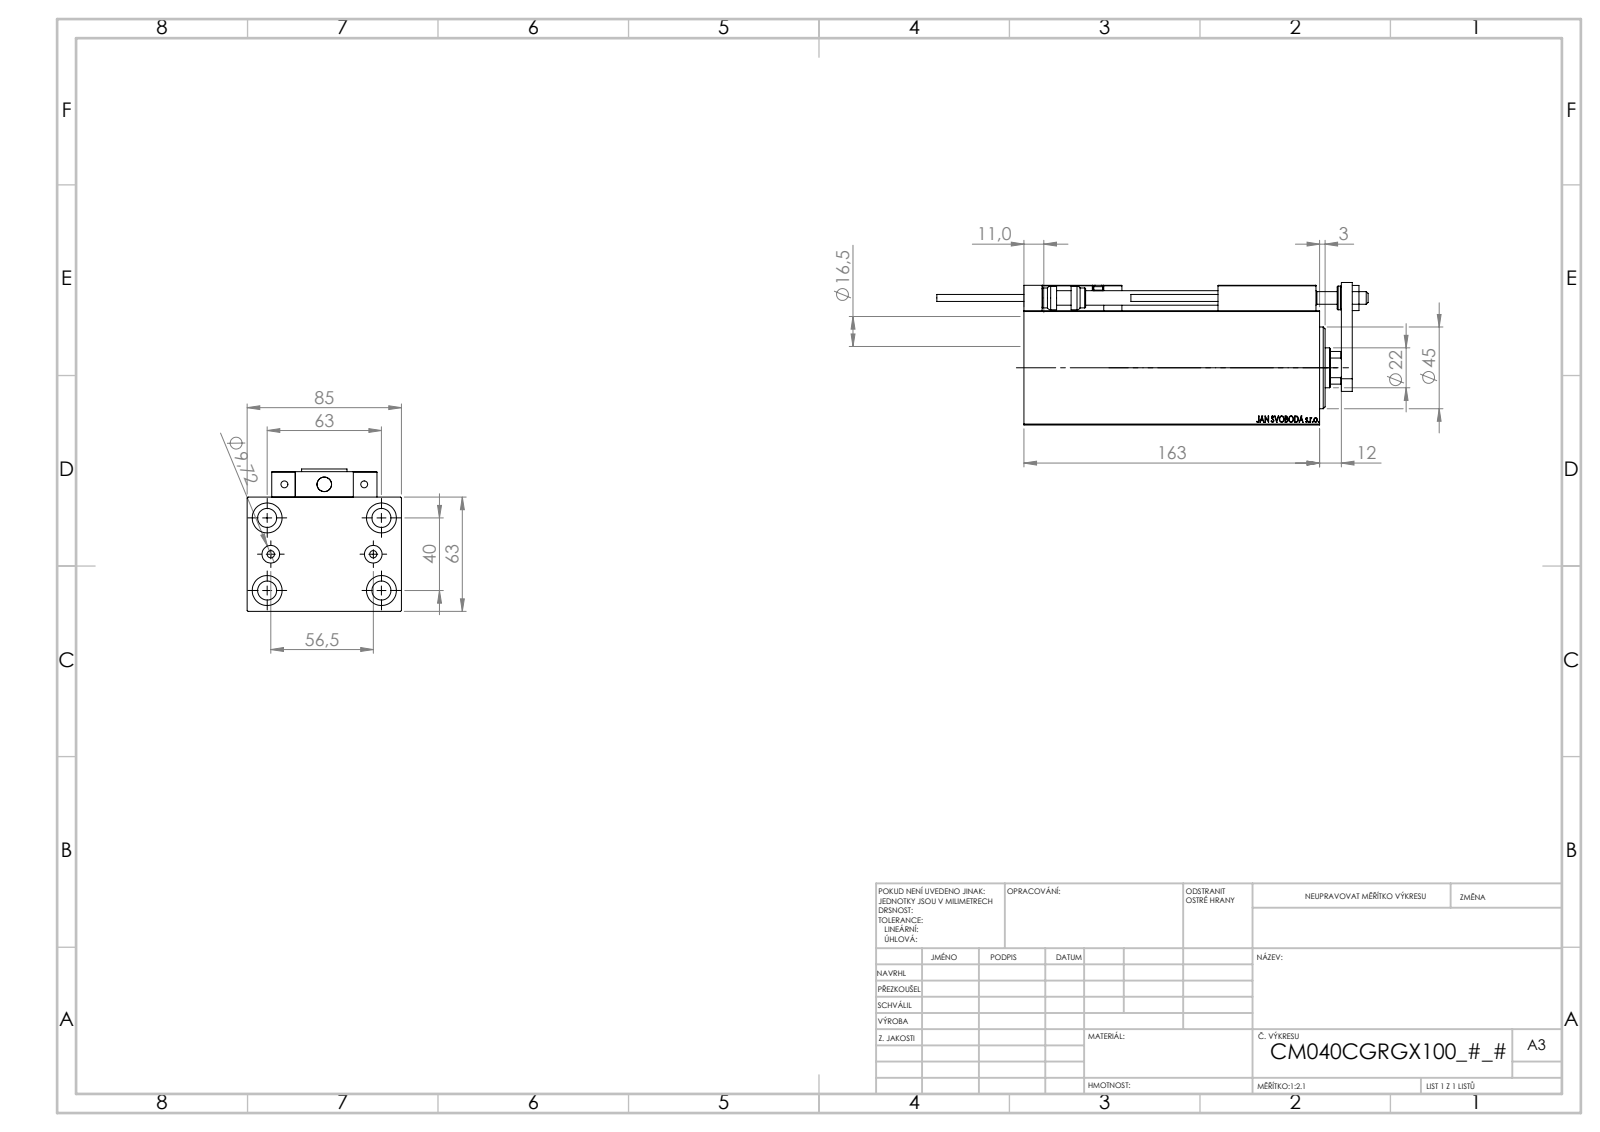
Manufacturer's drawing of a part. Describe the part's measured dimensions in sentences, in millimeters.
The part is named "ZARAZKA; Block; KONCOVKA; SWITCH X (+7 more)". Its 3-D file was written by "SolidWorks 2019 (CONFIG_CONTROL_DESIGN)". It is 23 solids with 1278 faces: 560 planar, 184 cylindrical and 534 other. Overall it measures 237.7 by 85 by 78.5 millimeters. Its volume is 769 623 cubic millimeters and its surface area 153 412 square millimeters. Round holes: 6 of diameter 4, 5 of diameter 8, 5 of diameter 16.5, 4 of diameter 3.2, 4 of diameter 10.5, 2 of diameter 5, 2 of diameter 9.72, 1 of diameter 7, 1 of diameter 12.5, 1 of diameter 22, 1 of diameter 25.5, 1 of diameter 40. Round bosses or shafts: 2 of diameter 5, 2 of diameter 3.8, 1 of diameter 13, 1 of diameter 11. Partial cylindrical surfaces (rounded edges, fillets, slot ends): 30 of radius 0.3, 2 of radius 3, 1 of radius 10.5. The main face-to-face distances are 63, 85, 12, 151, 163, 14, 77, 15, 18, 30. The hole center spacings are 37.31, 11.37, 20, 20.1, 20.5, 29.59, 29.69, 36.06.
